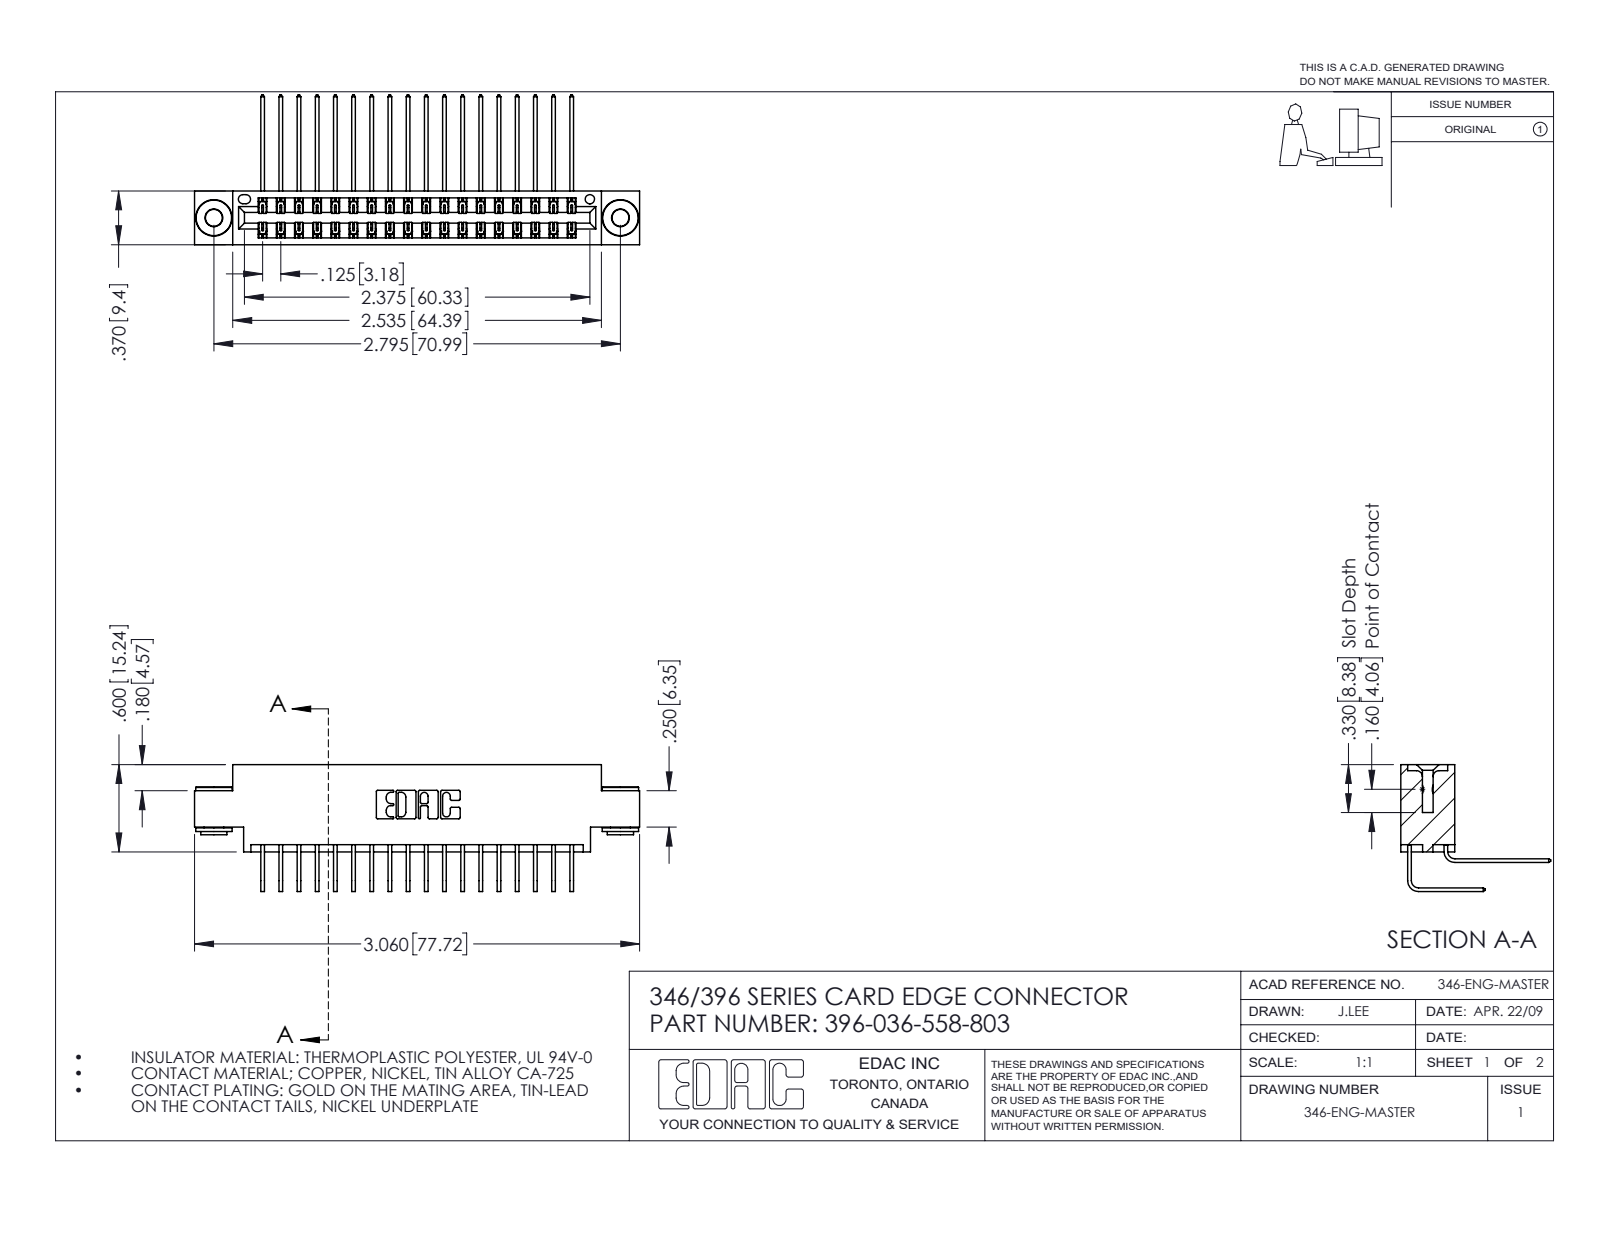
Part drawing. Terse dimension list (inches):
name: 346 Part_0.170 Offset - 0.156 Dia-TH; 345-250-002_345-250-002-102; 396-036-558-803; 345-292-001_558 Tail - 2 (+1 more)
written by: SolidWorks 2016 (CONFIG_CONTROL_DESIGN)
unit: in
bodies: 39 solids, 2108 faces (1422 planar, 678 cylindrical, 8 other)
size: 3.06 × 1.03 × 0.873
volume: 0.456 in³; area: 17.47 in²
holes: 2× ⌀0.116, 2× ⌀0.156, 1× ⌀0.064
bosses: 2× ⌀0.25, 2× ⌀0.18, 2× ⌀0.136
rounds: 54× R0.006, 22× R0.01, 6× R0.007, 6× R0.031, 3× R0.026, 2× R0.014, 2× R0.022, 2× R0.024
face distances: 0.322, 0.048, 0.37, 0.25, 0.025, 0.298, 0.072, 0.275, 0.148, 0.222
hole spacings: 0.246, 2.588, 2.795
